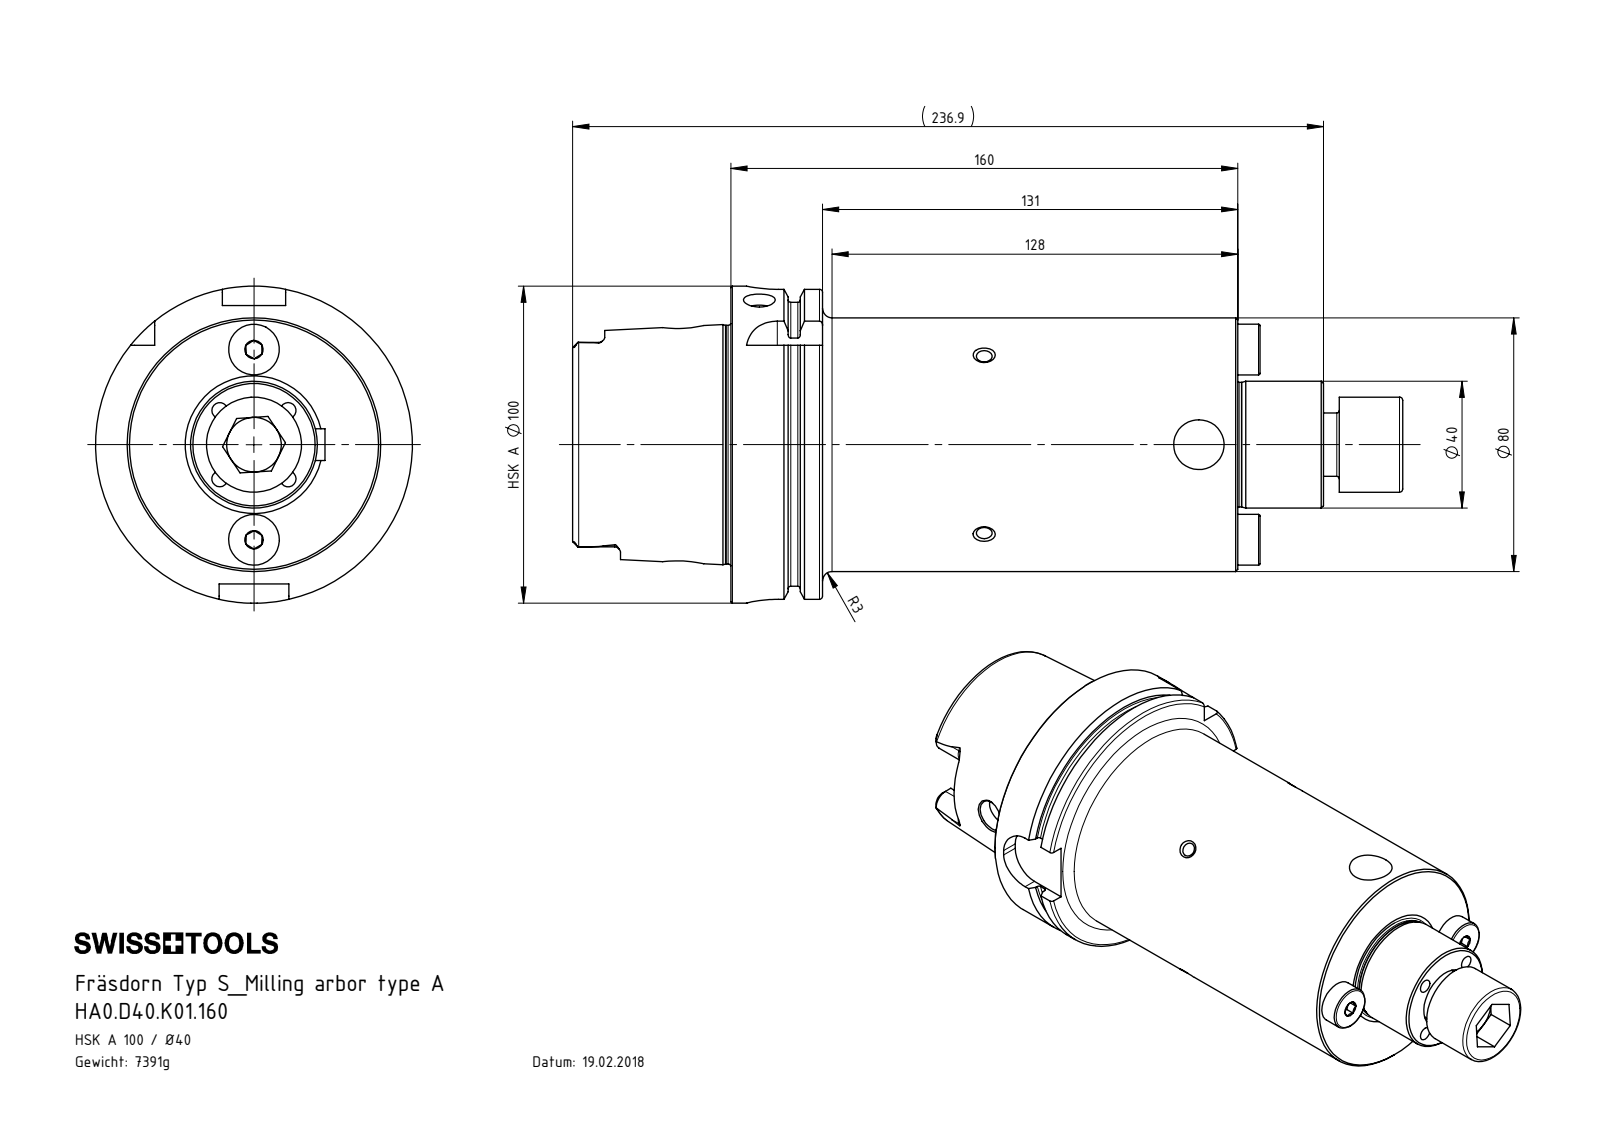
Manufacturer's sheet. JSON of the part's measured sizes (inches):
{"part_name": "HA0.D40.K01.160; D40-ER1.002.040_A; HA0-D40.K01.160_D_Fertigbearbeitung; D40-ER2.001.023_B (+1 more)", "step_written_by": "SolidWorks 2017 (AUTOMOTIVE_DESIGN)", "units": "inches", "bodies": {"solids": 5, "faces": 369, "planar": 89, "cylindrical": 119, "other": 161}, "overall_size": [10.311, 3.937, 3.937], "volume_in3": 57.46, "surface_area_in2": 166.5, "round_holes": [[0.197, 12], [0.394, 3], [0.472, 2], [0.551, 2], [0.689, 1], [0.827, 1], [0.886, 1], [1.024, 1], [2.087, 1], [2.48, 1]], "round_bosses_or_shafts": [[0.63, 2], [0.236, 2], [0.181, 2], [3.937, 1], [3.62, 1], [3.15, 1], [2.963, 1], [1.575, 1]], "partial_cylinders_radius": [[0.075, 6], [0.192, 4], [0.197, 4], [0.394, 4]], "face_to_face_distances": [6.299, 1.14, 5.159, 0.49, 0.65, 5.809, 1.965, 2.455, 3.104, 8.264], "hole_center_spacings": [0.6, 0.849, 0.868, 1.661, 2.719, 1.181, 1.2, 2.362]}
